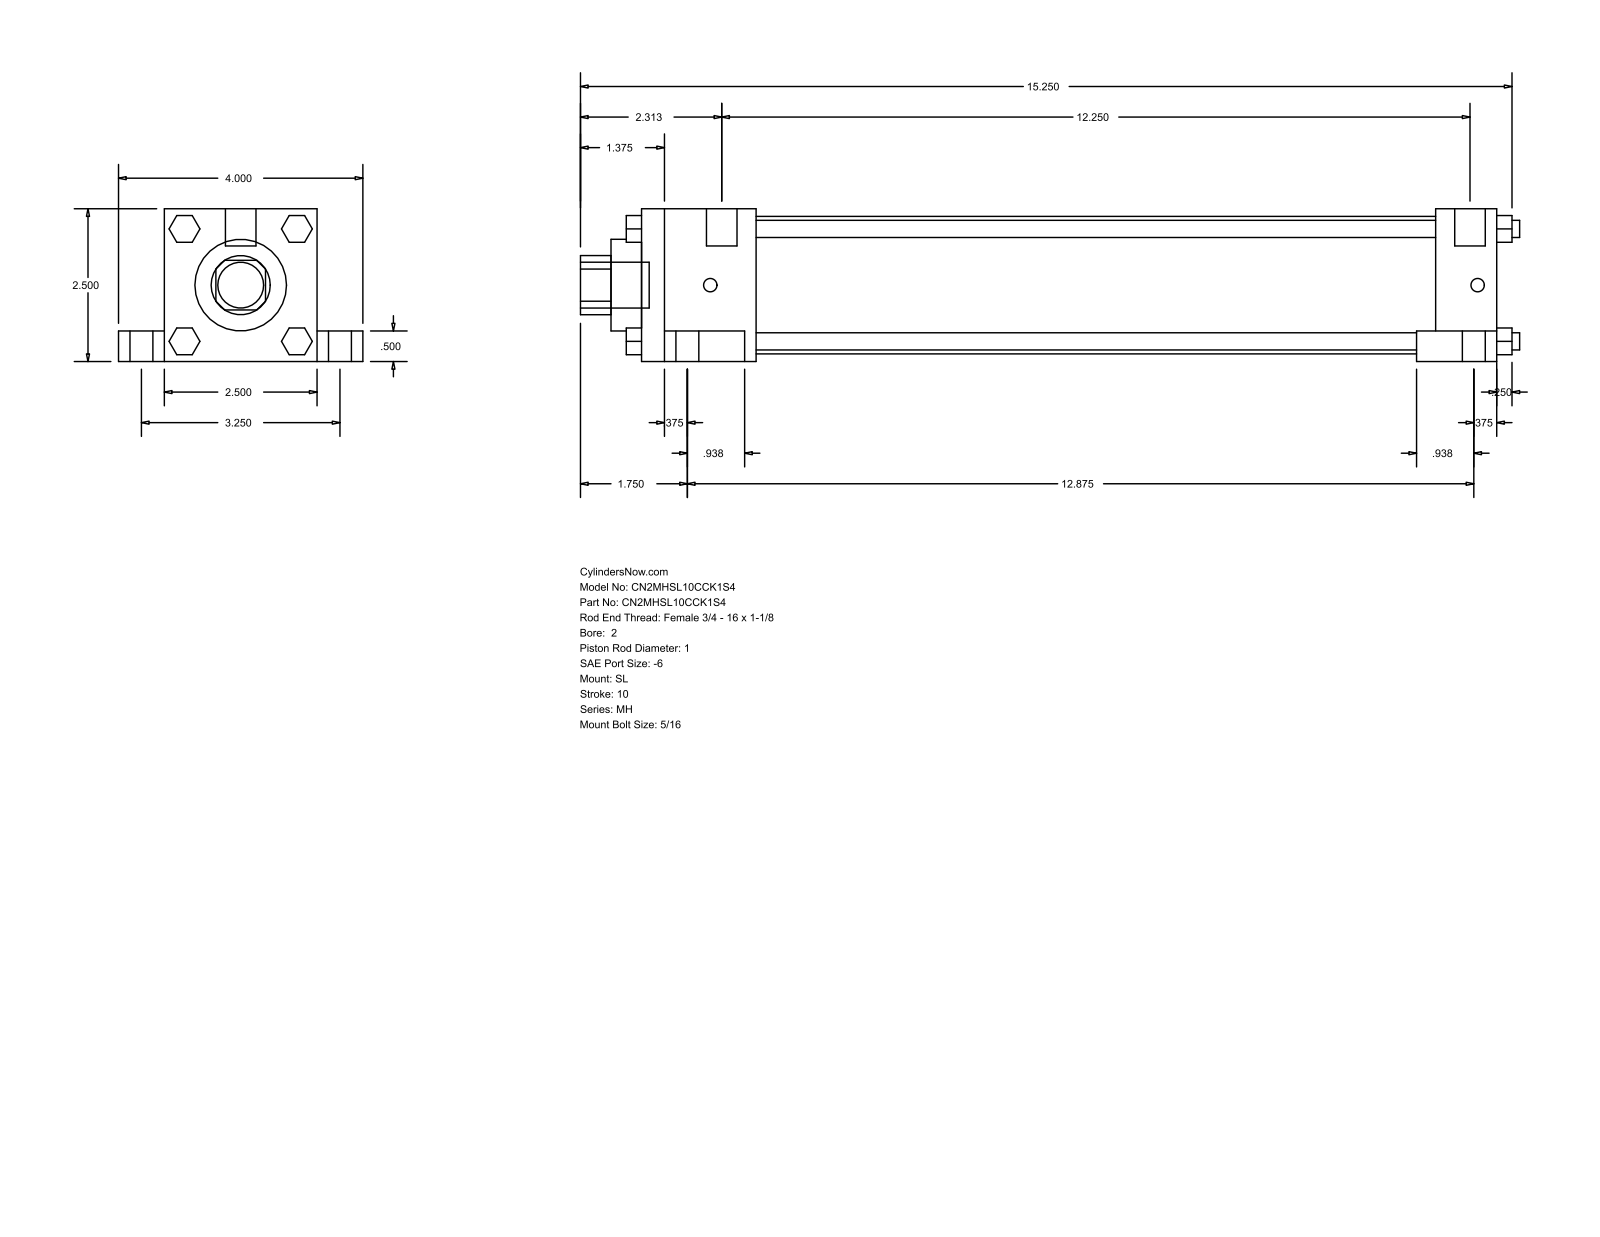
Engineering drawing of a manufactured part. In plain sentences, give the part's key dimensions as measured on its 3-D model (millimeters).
The part is named "MH_SL__0200_1". Its 3-D file was written by "GSSL Pune (CONFIG_CONTROL_DESIGN)". It is 0 solids with 148 faces: 112 planar, 36 cylindrical and 0 other. Overall it measures 390.52 by 101.6 by 63.5 millimeters. Round holes: 1 of diameter 25.4, 1 of diameter 38.1, 1 of diameter 57.15. Round bosses or shafts: 4 of diameter 15.88, 4 of diameter 9.53, 4 of diameter 7.14, 4 of diameter 5.56, 2 of diameter 12.7, 1 of diameter 19.05. Partial cylindrical surfaces (rounded edges, fillets, slot ends): 1 of radius 12.29. The main face-to-face distances are 63.5, 355.6, 12.7, 19.05, 50.8, 82.55, 9.52, 25.4, 330.2, 47.63.
